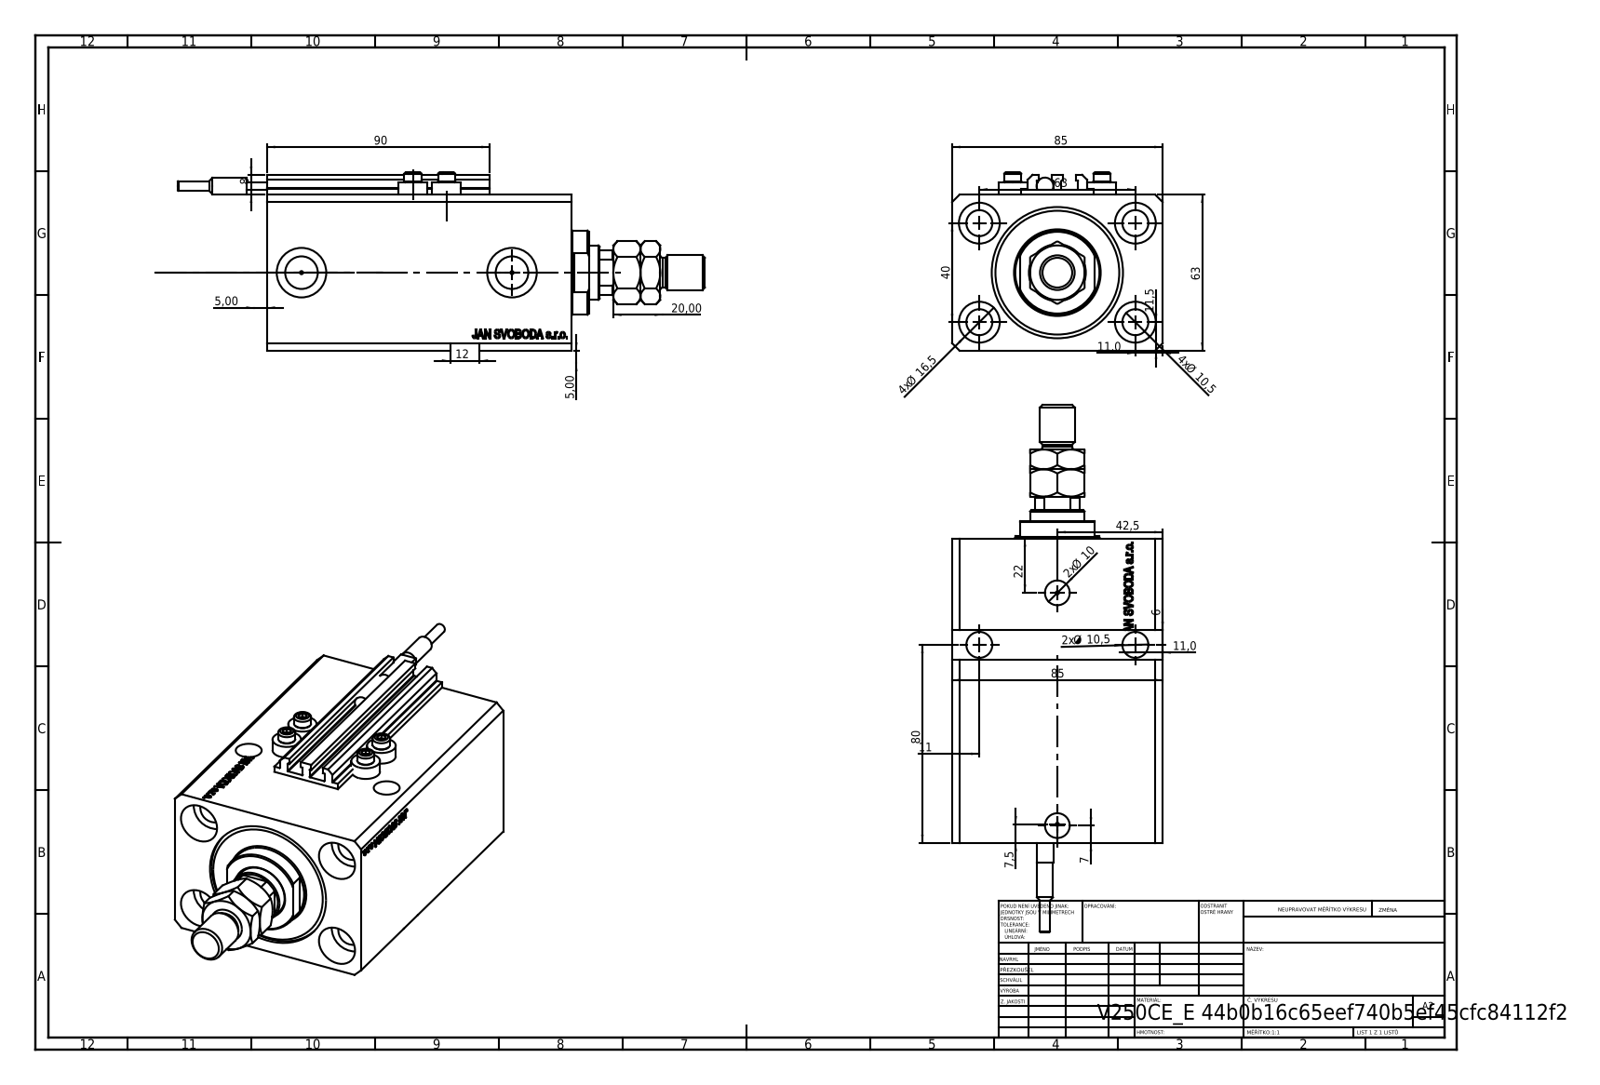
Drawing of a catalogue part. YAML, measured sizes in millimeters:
part_name: "MTA; V250CE_C_VCP; V250CE_VC_E; SWITCH_V250CE (+2 more)"
step_written_by: "SolidWorks 2019 (CONFIG_CONTROL_DESIGN)"
units: millimeters
bodies: {solids: 10, faces: 1162, planar: 566, cylindrical: 136, other: 460}
overall_size: [212.9, 85, 72]
volume: 576766
surface_area: 123861
round_holes:
  - {diameter: 10.5, count: 6}
  - {diameter: 1.25, count: 4}
  - {diameter: 4, count: 4}
  - {diameter: 16.5, count: 4}
  - {diameter: 10, count: 2}
  - {diameter: 13.16, count: 2}
  - {diameter: 20, count: 2}
  - {diameter: 12.5, count: 1}
  - {diameter: 22, count: 1}
  - {diameter: 40, count: 1}
  - {diameter: 53, count: 1}
round_bosses_or_shafts:
  - {diameter: 11.6, count: 4}
  - {diameter: 7, count: 4}
  - {diameter: 34, count: 1}
  - {diameter: 14, count: 1}
  - {diameter: 12, count: 1}
  - {diameter: 6.8, count: 1}
  - {diameter: 6.5, count: 1}
  - {diameter: 4, count: 1}
partial_cylinders:
  - {radius: 0.2, count: 10}
  - {radius: 10.5, count: 1}
face_to_face_distances: [63, 85, 123, 95.9, 27.1, 11.4, 84.5, 111.6, 3, 65]
hole_center_spacings: [37.31, 63, 13.6, 15.4, 24.96, 33.62, 36, 37.86]
